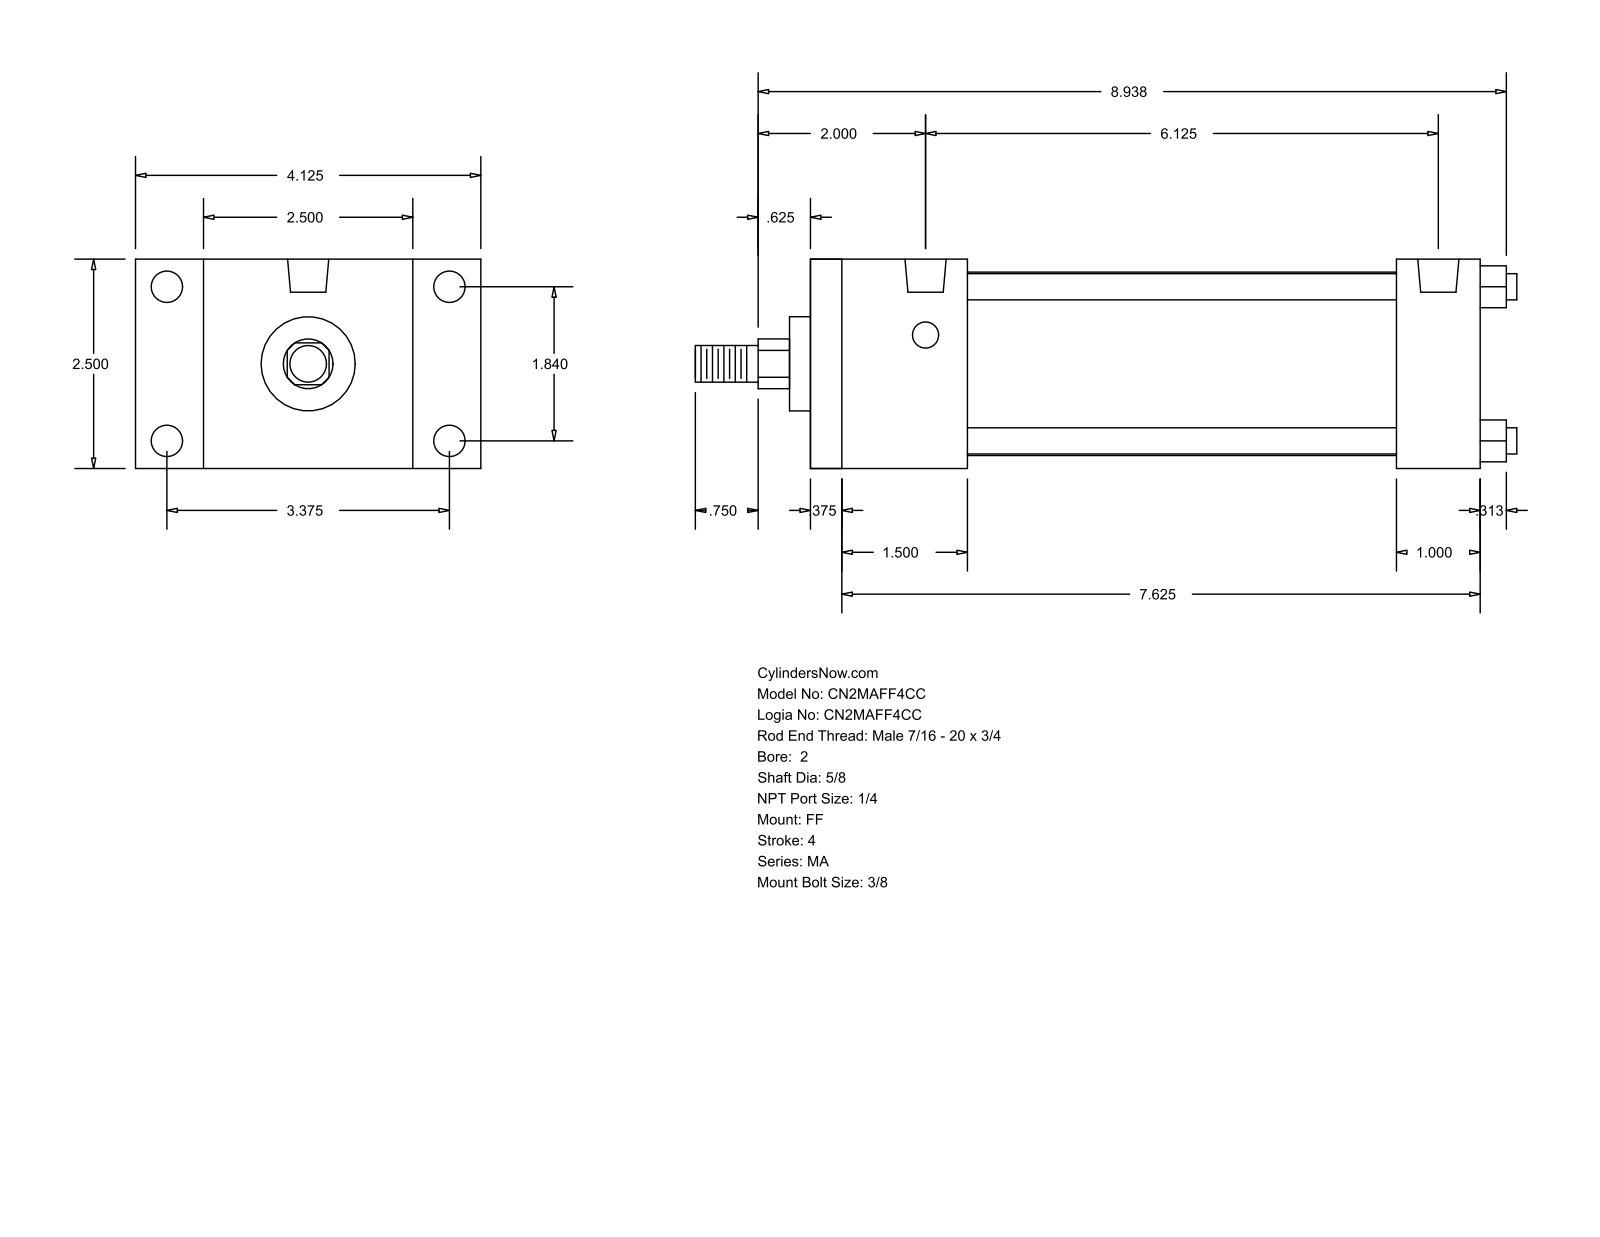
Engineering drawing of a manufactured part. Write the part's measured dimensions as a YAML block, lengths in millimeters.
part_name: "MA_FF__0200_0.625"
step_written_by: "GSSL Pune (CONFIG_CONTROL_DESIGN)"
units: millimeters
bodies: {solids: 0, faces: 92, planar: 64, cylindrical: 28, other: 0}
overall_size: [249.24, 104.78, 63.5]
round_holes:
  - {diameter: 7.94, count: 4}
  - {diameter: 9.53, count: 4}
  - {diameter: 12.49, count: 2}
round_bosses_or_shafts:
  - {diameter: 7.94, count: 4}
  - {diameter: 55.63, count: 1}
  - {diameter: 28.57, count: 1}
  - {diameter: 15.88, count: 1}
  - {diameter: 11.11, count: 1}
partial_cylinders:
  - {radius: 7.54, count: 1}
face_to_face_distances: [63.5, 203.19, 9.52, 193.67, 38.1, 47.62, 177.8, 168.28, 130.18, 155.57]
hole_center_spacings: [46.74, 85.72, 97.63, 155.58]
